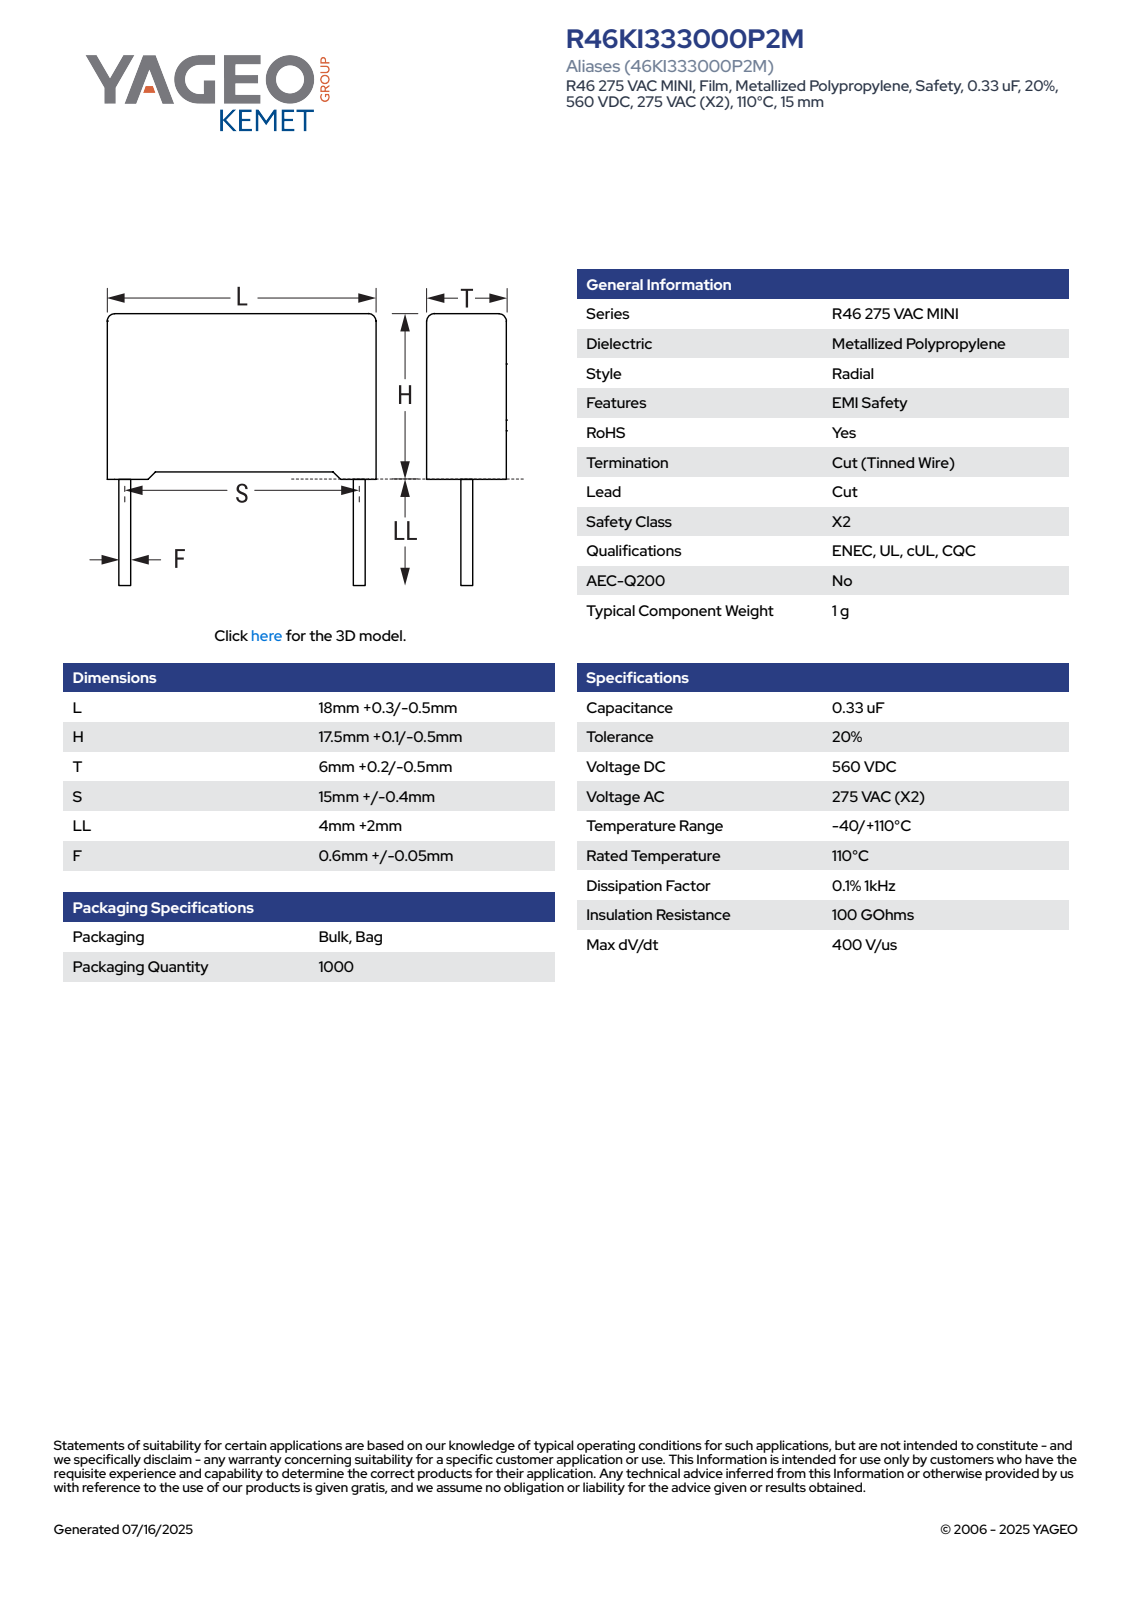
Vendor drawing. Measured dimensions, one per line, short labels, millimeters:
name: CFR_RB2_18X17.5X6_L18.3H17.6T6.2S15LL6F0.65
written by: SolidWorks 2021 (AUTOMOTIVE_DESIGN)
unit: mm
bodies: 4 solids, 85 faces (77 planar, 8 cylindrical, 0 other)
size: 23.6 × 18.3 × 6.21
volume: 1 927 mm³; area: 1 137 mm²
bosses: 2× ⌀0.65
rounds: 4× R0.5
face distances: 6.2, 18.3, 16.85, 0.61, 0.75, 17.6, 16.99, 5.59, 17.69, 4.98
